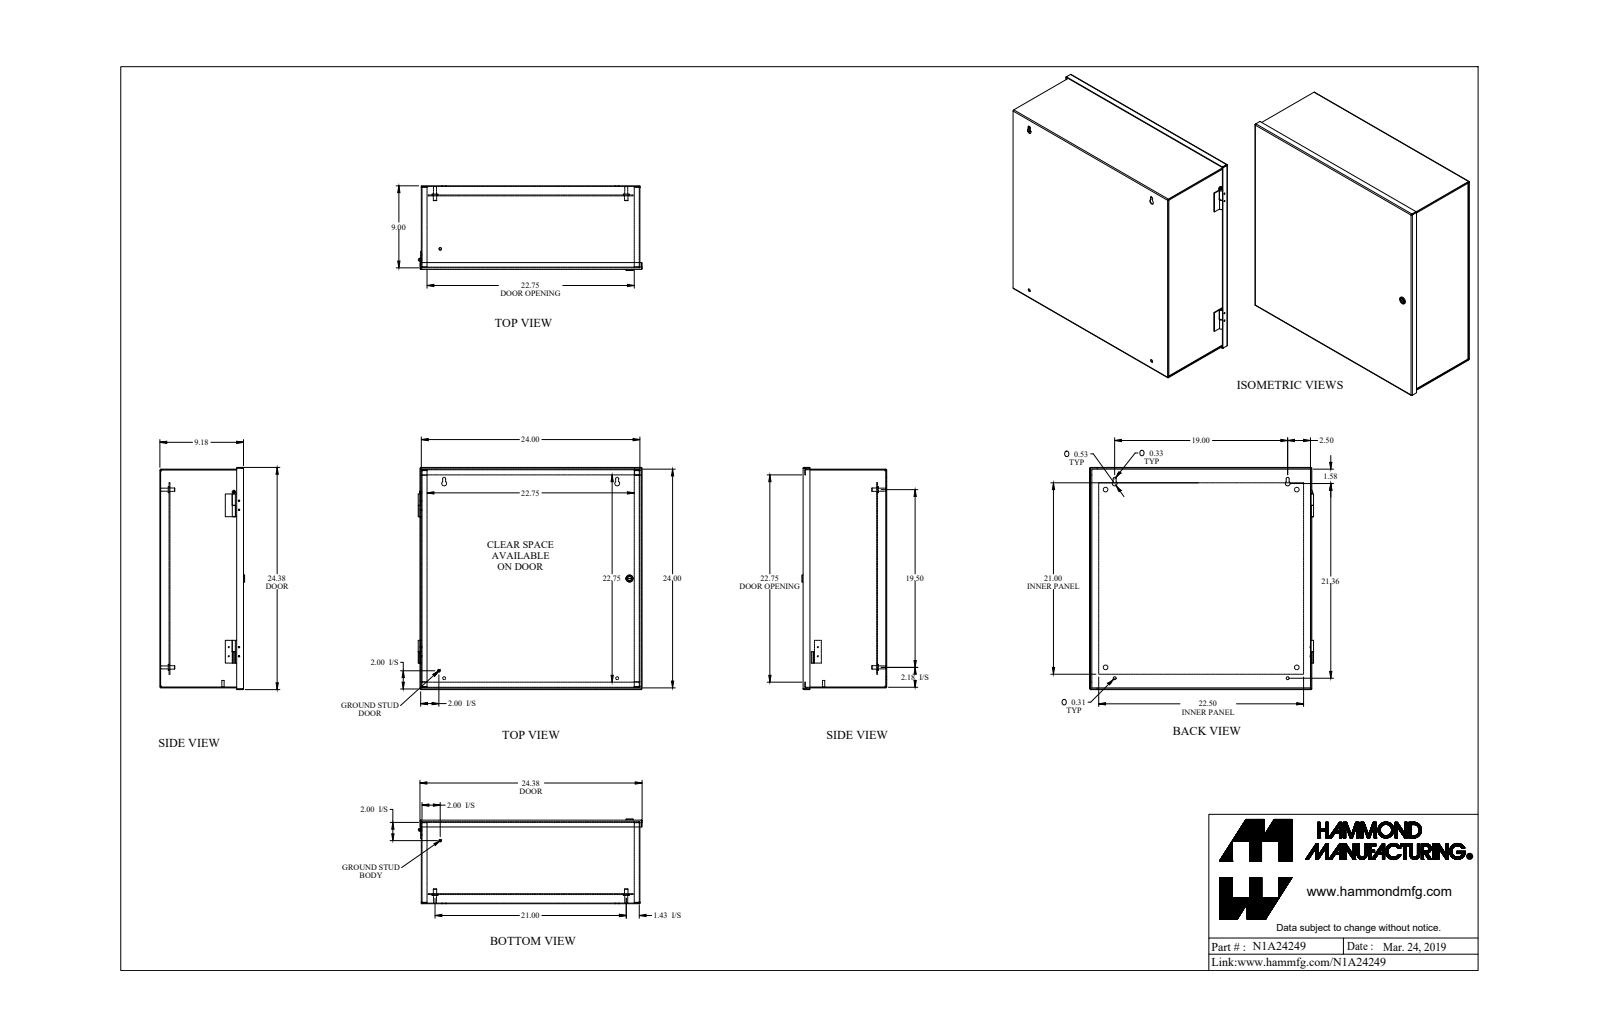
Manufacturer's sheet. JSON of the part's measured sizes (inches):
{"part_name": "N1A24249", "step_written_by": "SolidWorks 2018 (AUTOMOTIVE_DESIGN)", "units": "inches", "bodies": {"solids": 23, "faces": 520, "planar": 294, "cylindrical": 182, "other": 44}, "overall_size": [24.574, 24.384, 9.299], "volume_in3": 204, "surface_area_in2": 5384, "round_holes": [[0.14, 8], [0.5, 4], [0.307, 2], [0.312, 2], [0.445, 2], [0.17, 1], [0.187, 1], [0.516, 1]], "round_bosses_or_shafts": [[0.128, 8], [0.375, 5], [0.65, 4], [0.33, 4], [1, 2], [0.281, 2], [0.25, 2], [0.788, 1]], "partial_cylinders_radius": [[0.036, 16], [0.108, 16], [0.06, 2], [0.153, 2], [0.164, 2], [0.266, 2], [0.03, 1], [0.125, 1]], "face_to_face_distances": [0.072, 9.105, 23.928, 9.033, 9.177, 1.104, 1.032, 8.001, 8.073, 1.009], "hole_center_spacings": [1, 1.119, 1.553, 2.031, 9.757, 16.062, 16.062, 16.1]}
